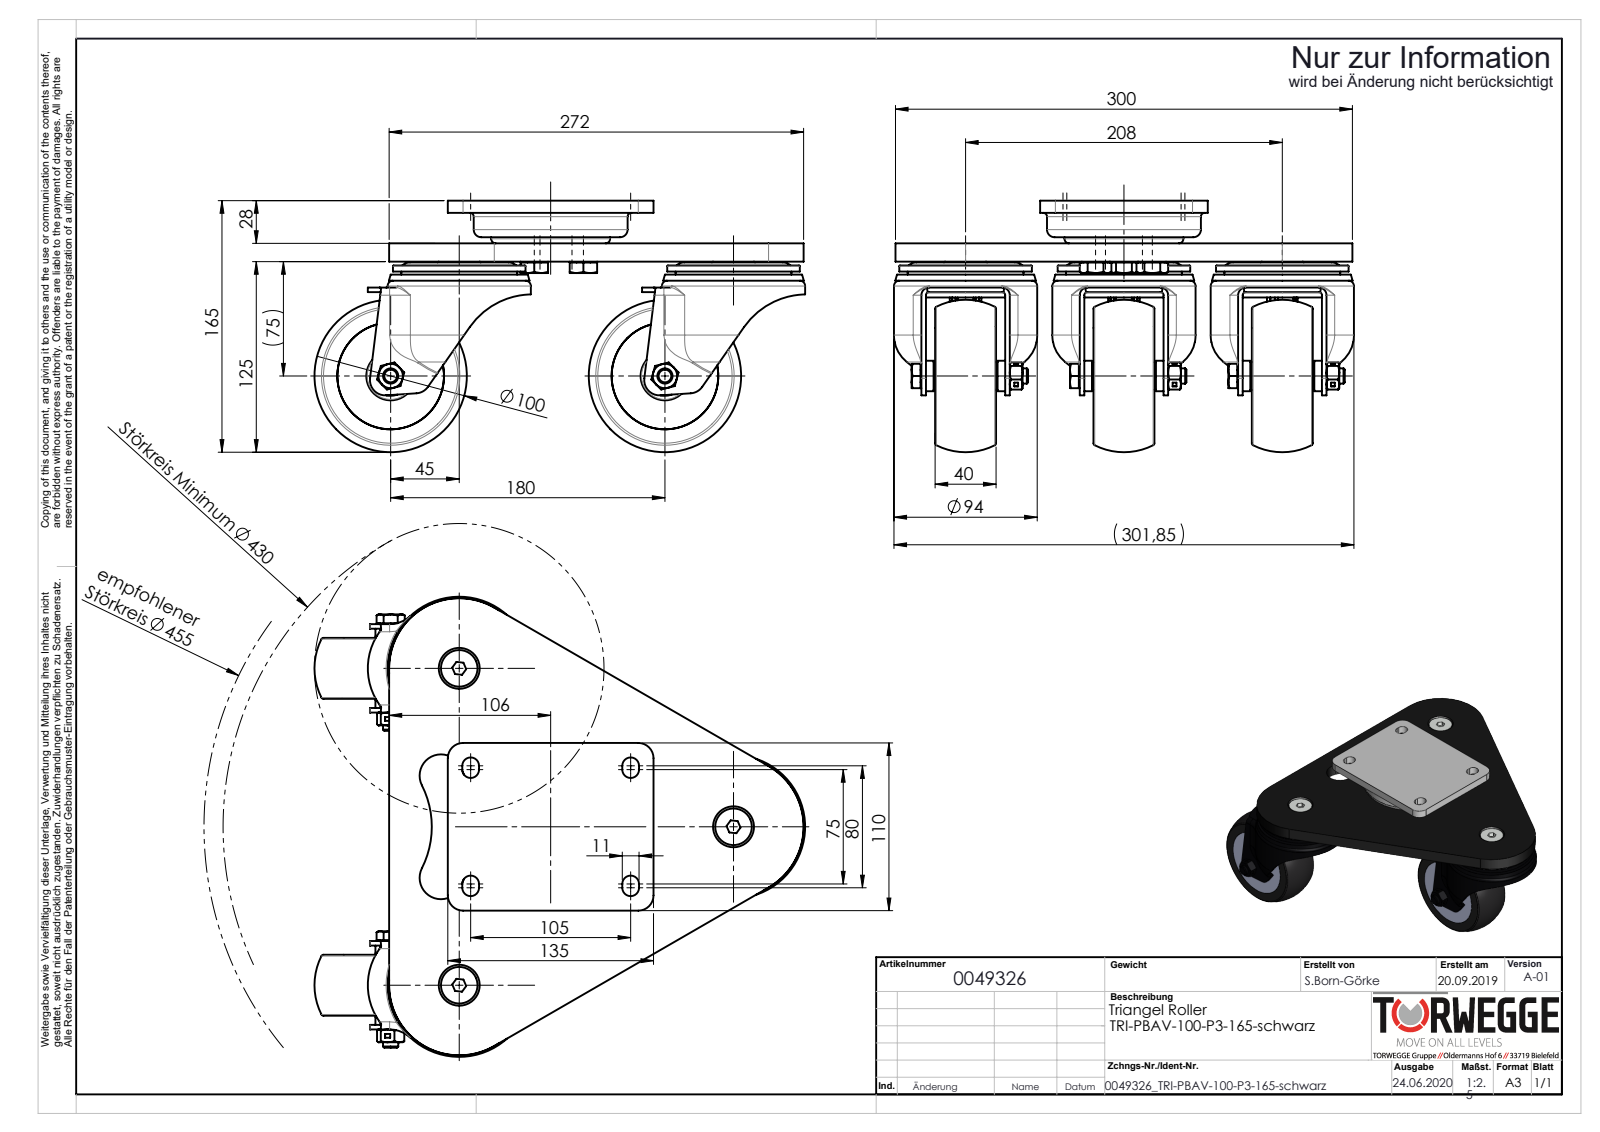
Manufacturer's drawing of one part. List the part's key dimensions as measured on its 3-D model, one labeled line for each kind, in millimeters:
Part name (STEP PRODUCT): 0049326
STEP written by: SolidWorks 2018 (AUTOMOTIVE_DESIGN)
Units: millimetres
Bodies: 62 solids, 1326 faces (456 planar, 441 cylindrical, 429 other)
Overall size (bounding box): 322 × 301.85 × 165
Volume: 2 156 000 mm³ · Surface area: 503 276 mm²
Round holes (diameter × count): ⌀12 ×7, ⌀10.2 ×6, ⌀13 ×5, ⌀12.7 ×3, ⌀13.5 ×3, ⌀30 ×3, ⌀88 ×3, ⌀8.5 ×2, ⌀10 ×2, ⌀10.02 ×2, ⌀10.1 ×2, ⌀26 ×2
Round bosses / shafts (diameter × count): ⌀18 ×5, ⌀94 ×3, ⌀87 ×3, ⌀76 ×3, ⌀62 ×3, ⌀28.5 ×3, ⌀24 ×3, ⌀11.79 ×3
Partial cylindrical surfaces — rounded edges, fillets, slot ends (radius × count): R5 ×9, R5.5 ×8, R10 ×8, R2 ×6, R41.04 ×3, R46 ×3, R14 ×2, R50 ×2
Main face-to-face distances: 12, 103.92, 40, 207.84, 28, 6, 9, 49, 63.92, 143.92
Hole centre spacings: 132.07, 37.24, 98.5, 207.84, 180
